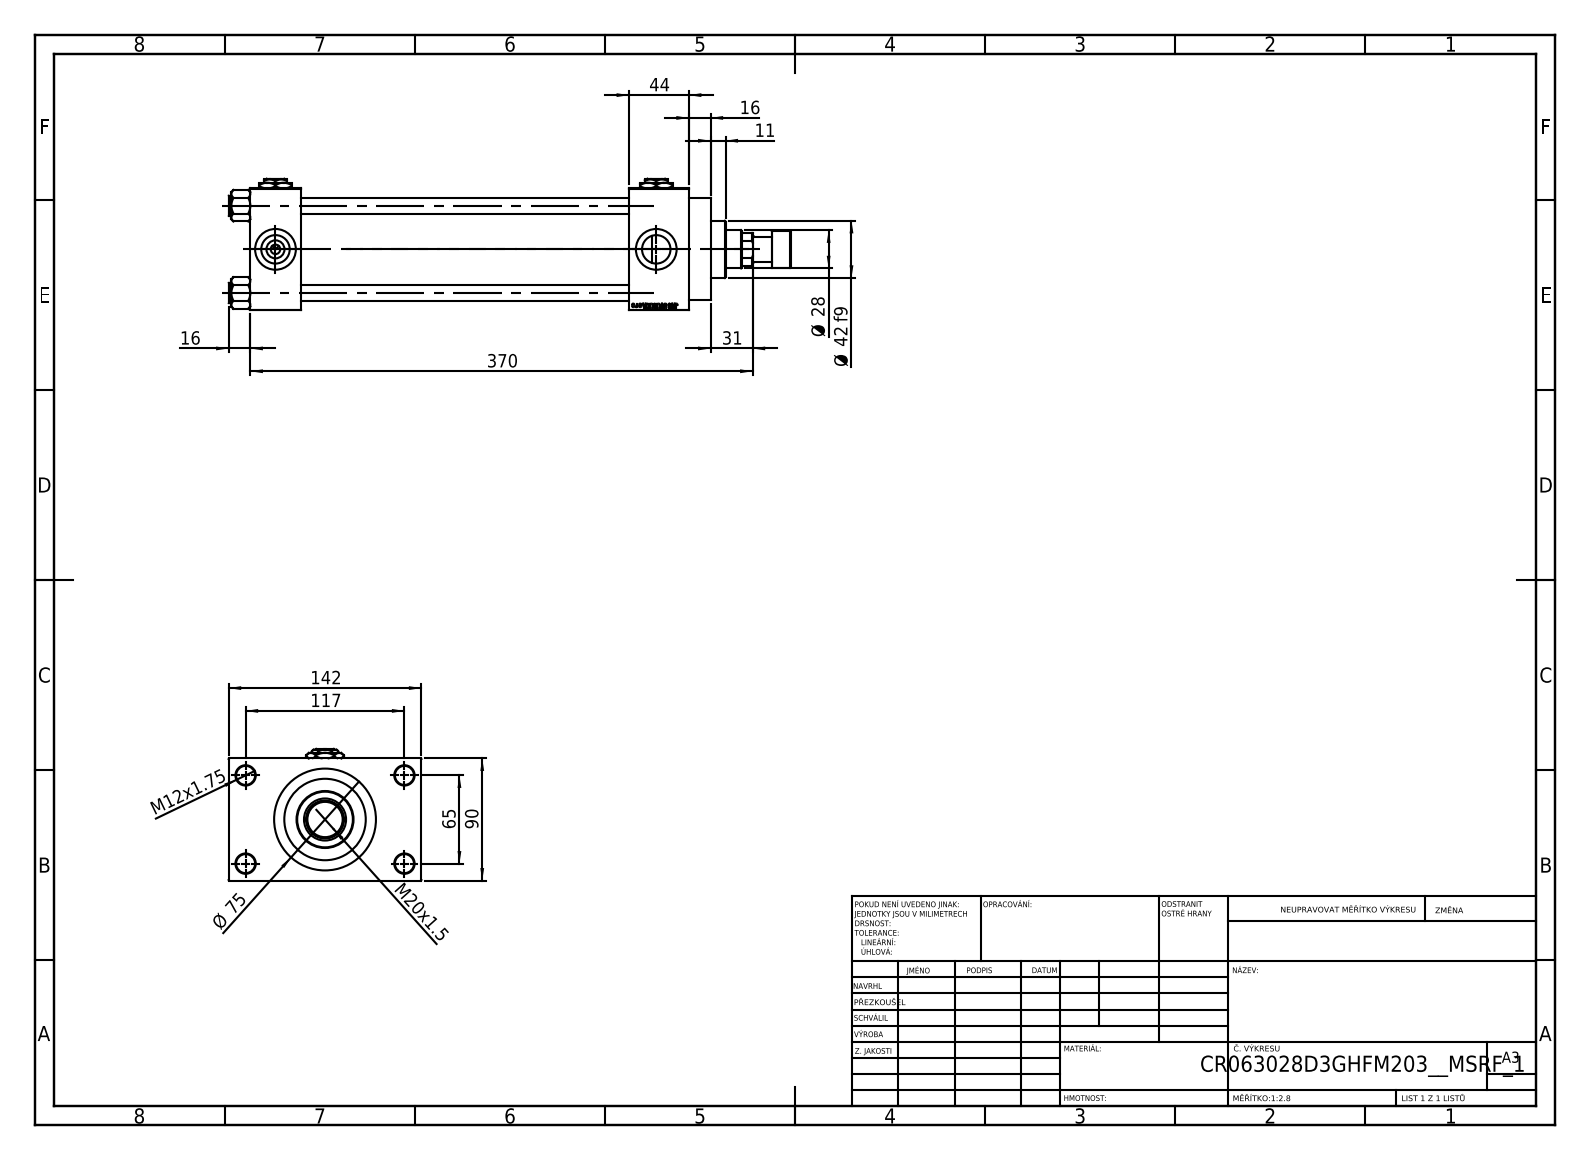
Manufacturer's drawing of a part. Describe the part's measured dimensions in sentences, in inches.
The part is named "V215CR_ROD_END_F; V215CR_VCP_D; NUT_M5_D; V215CR_D_TYCINKA (+3 more)". Its 3-D file was written by "SolidWorks 2019 (CONFIG_CONTROL_DESIGN)". It is 14 solids with 1218 faces: 549 planar, 103 cylindrical and 566 other. Overall it measures 16.299 by 5.591 by 3.819 inches. Its volume is 86.17 cubic inches and its surface area 508.1 square inches. Round holes: 4 of diameter 0.472, 4 of diameter 0.551, 4 of diameter 0.825, 4 of diameter 1.181, 3 of diameter 0.276, 1 of diameter 0.728, 1 of diameter 1.102, 1 of diameter 1.22, 1 of diameter 1.969, 1 of diameter 2.362, 1 of diameter 2.48. Round bosses or shafts: 4 of diameter 0.591, 1 of diameter 2.953, 1 of diameter 2.717, 1 of diameter 1.654, 1 of diameter 1.063, 1 of diameter 0.709. The main face-to-face distances are 3.543, 9.528, 1.457, 10.984, 11.26, 12.717, 1.732, 1.024, 4.567, 0.63. The hole center spacings are 1.037, 1.79, 2.531, 2.635, 2.748, 3.569, 4.383, 2.559.
